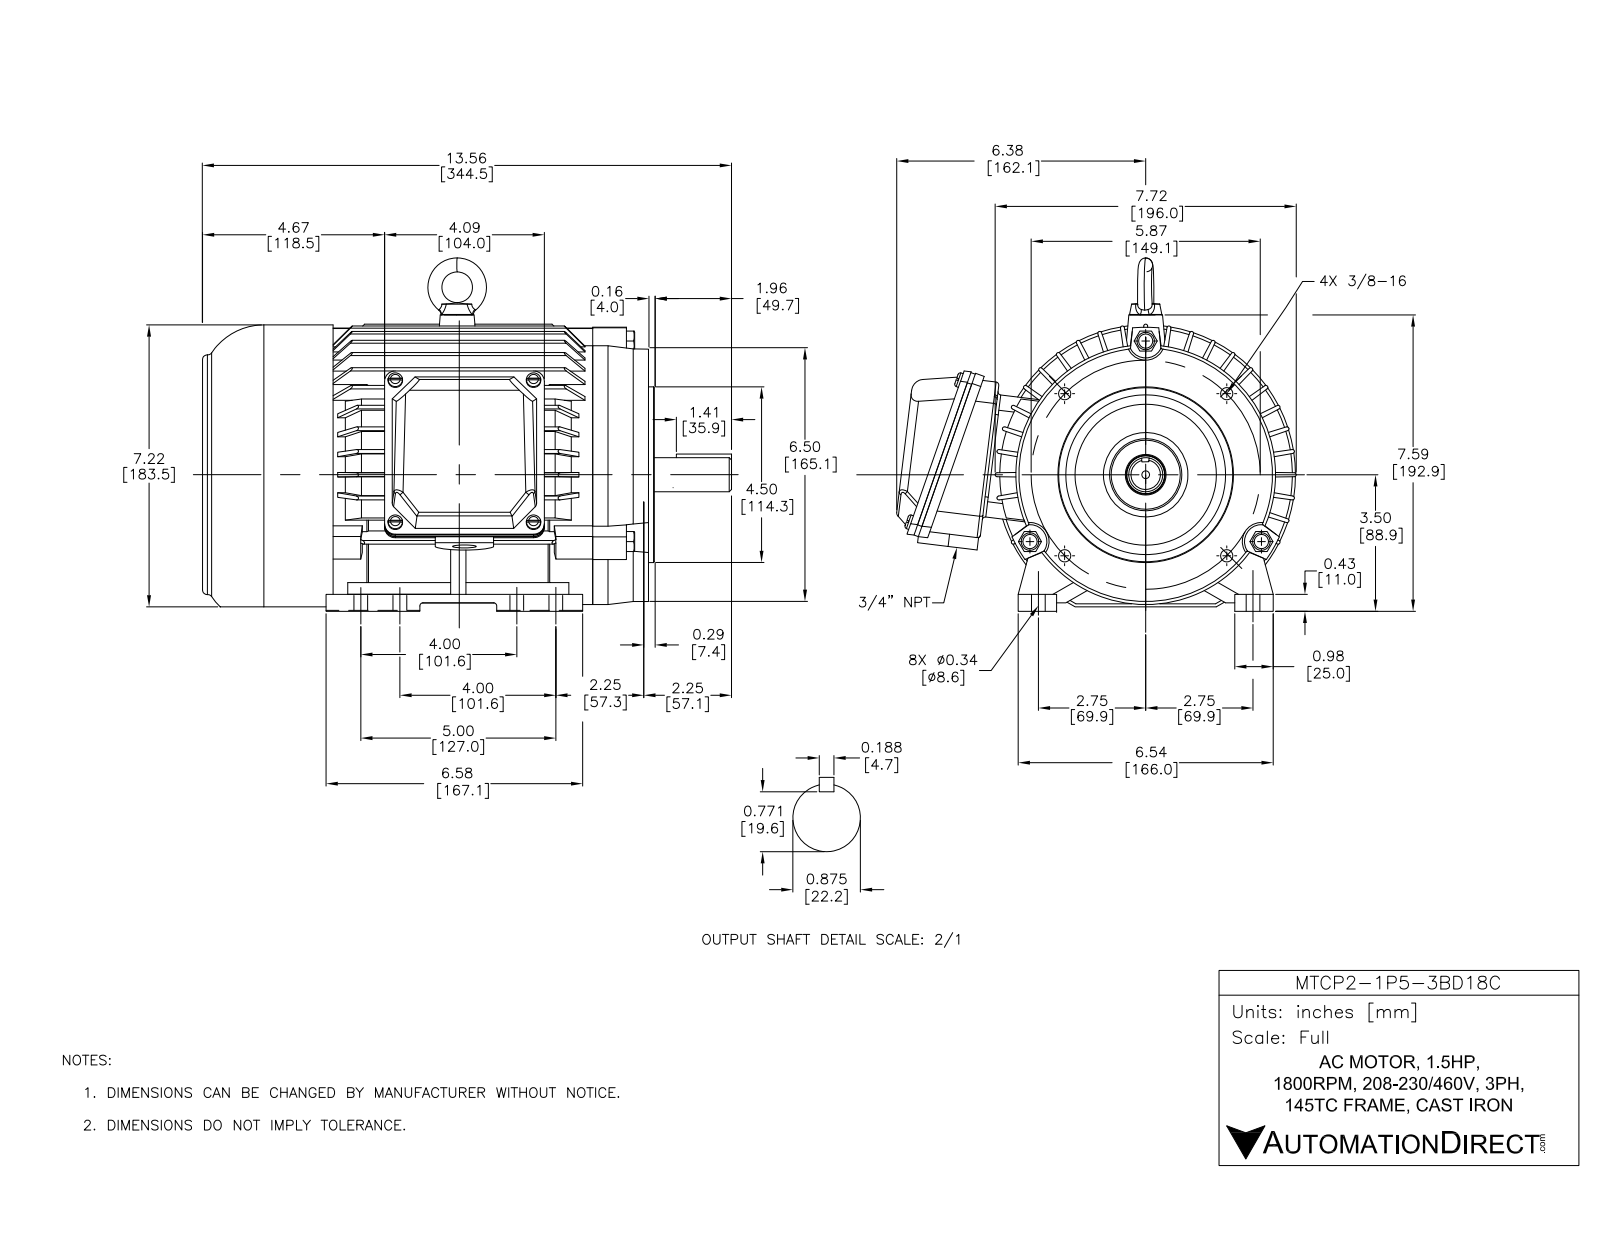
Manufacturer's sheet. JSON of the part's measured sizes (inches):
{"part_name": "PEWWE-145TC", "step_written_by": "SolidWorks 2017 (AUTOMOTIVE_DESIGN)", "units": "inches", "bodies": {"solids": 14, "faces": 1427, "planar": 650, "cylindrical": 561, "other": 216}, "overall_size": [13.559, 10.242, 9.055], "volume_in3": 329, "surface_area_in2": 959.8, "round_holes": [[0.228, 8], [0.354, 8], [0.165, 4], [0.197, 4], [0.313, 4], [0.326, 4], [0.362, 3], [0.394, 3], [0.268, 1], [0.276, 1], [0.315, 1], [0.61, 1]], "round_bosses_or_shafts": [[0.315, 4], [0.197, 4], [0.283, 3], [7.677, 1], [7.52, 1], [6.654, 1], [6.575, 1], [6.496, 1]], "partial_cylinders_radius": [[0.02, 224], [0.05, 26], [0.079, 24], [0.276, 16], [0.118, 10], [0.236, 4], [0.394, 4], [0.197, 2]], "face_to_face_distances": [0.039, 6.89, 0.079, 0.157, 9.864, 2.974, 9.904, 6.85, 9.825, 9.943], "hole_center_spacings": [3.543, 2.126, 3.858, 5.239, 0.157, 1, 2.132, 2.937]}
